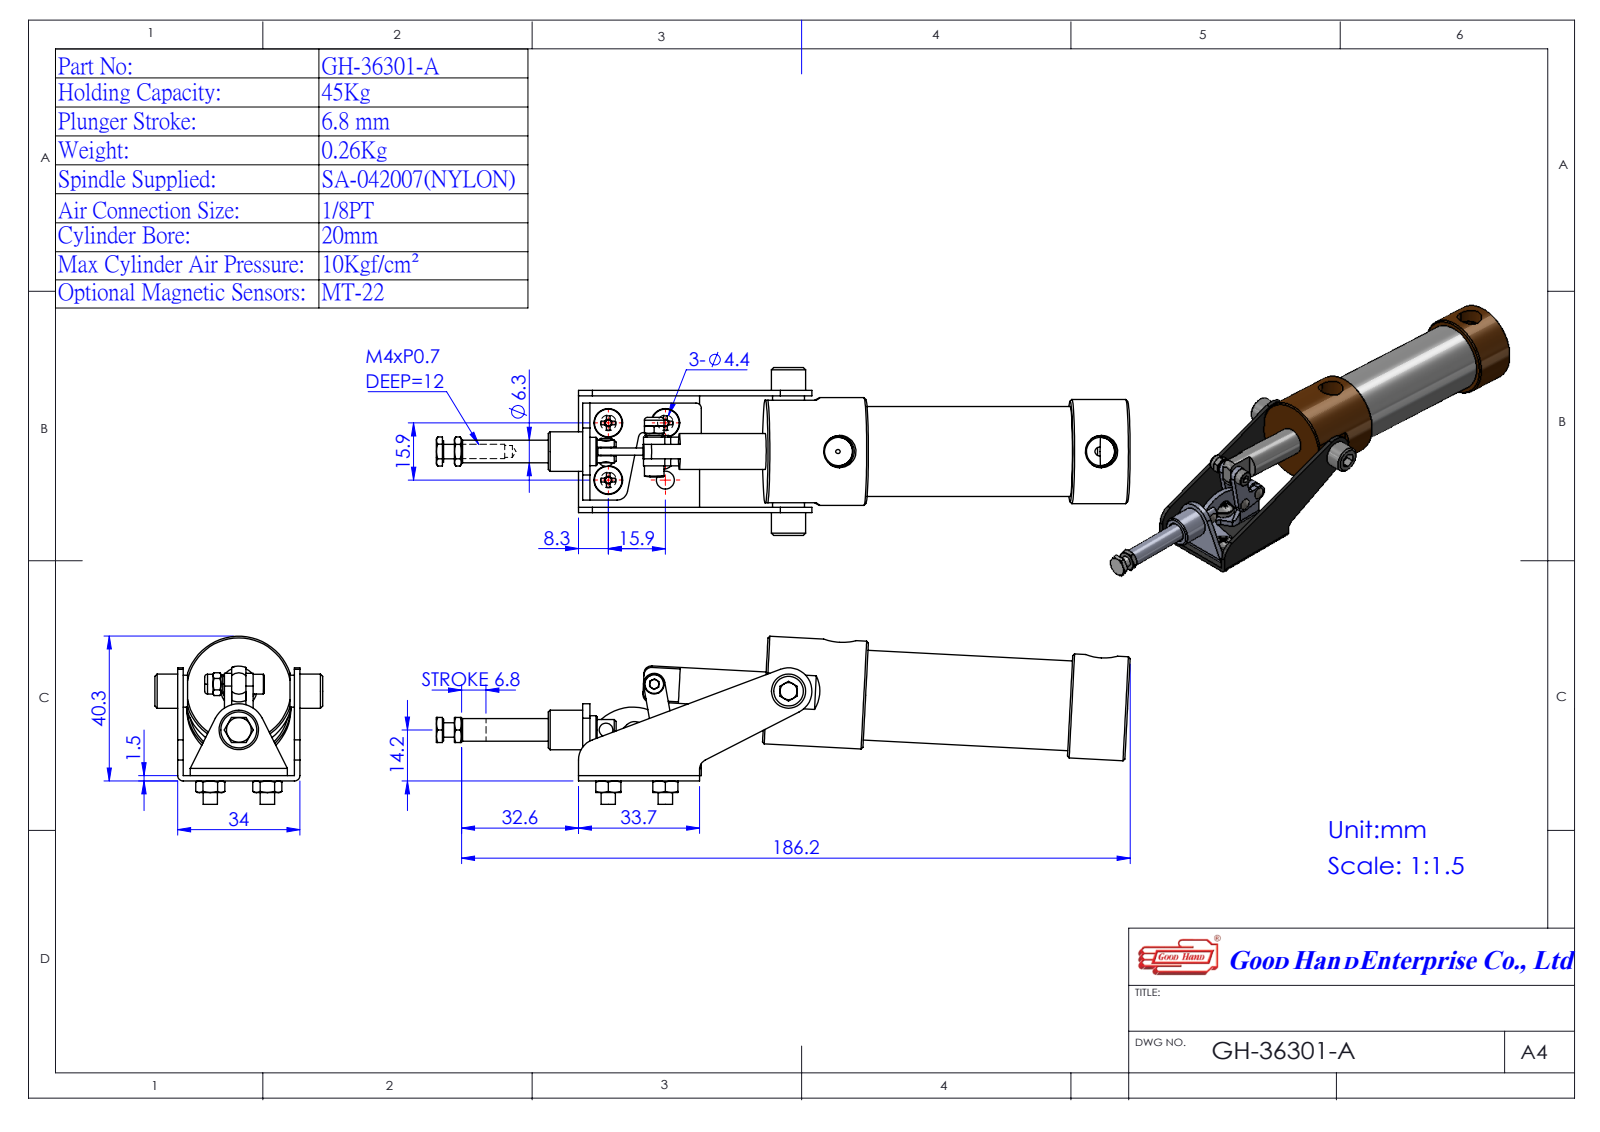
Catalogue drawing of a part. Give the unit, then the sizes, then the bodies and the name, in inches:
Units: inches
Overall size (bounding box): 7.569 × 1.921 × 1.839
Round holes (diameter × count): ⌀0.079 ×4, ⌀0.311 ×2, ⌀0.098 ×1, ⌀0.118 ×1, ⌀0.13 ×1, ⌀0.146 ×1, ⌀0.157 ×1, ⌀0.201 ×1, ⌀0.217 ×1, ⌀0.248 ×1, ⌀0.256 ×1, ⌀0.394 ×1
Round bosses / shafts (diameter × count): ⌀0.374 ×3, ⌀0.197 ×3, ⌀1.181 ×1, ⌀1.142 ×1, ⌀0.984 ×1, ⌀0.787 ×1, ⌀0.709 ×1, ⌀0.685 ×1
Partial cylindrical surfaces — rounded edges, fillets, slot ends (radius × count): R0.118 ×9, R0.059 ×2, R0.079 ×1, R0.236 ×1, R0.242 ×1, R0.256 ×1, R0.287 ×1, R0.512 ×1
Main face-to-face distances: 0.059, 1.28, 0.079, 1.22, 1.339, 0.63, 0.118, 0.689, 3.978, 0.571
Hole centre spacings: 0.295, 0.563, 0.63, 0.636, 0.726, 0.918, 1.163, 1.454
Volume: 3.499 in³ · Surface area: 52.22 in²
Bodies: 11 solids, 553 faces (239 planar, 146 cylindrical, 168 other)
Part name (STEP PRODUCT): Group6^GH-36301-A(簡化)-1; Group1^GH-36301-A(簡化)-1; Group3^GH-36301-A(簡化)-1; Group4^GH-36301-A(簡化)-1 (+4 more)
STEP written by: SolidWorks 2016 (AUTOMOTIVE_DESIGN)
